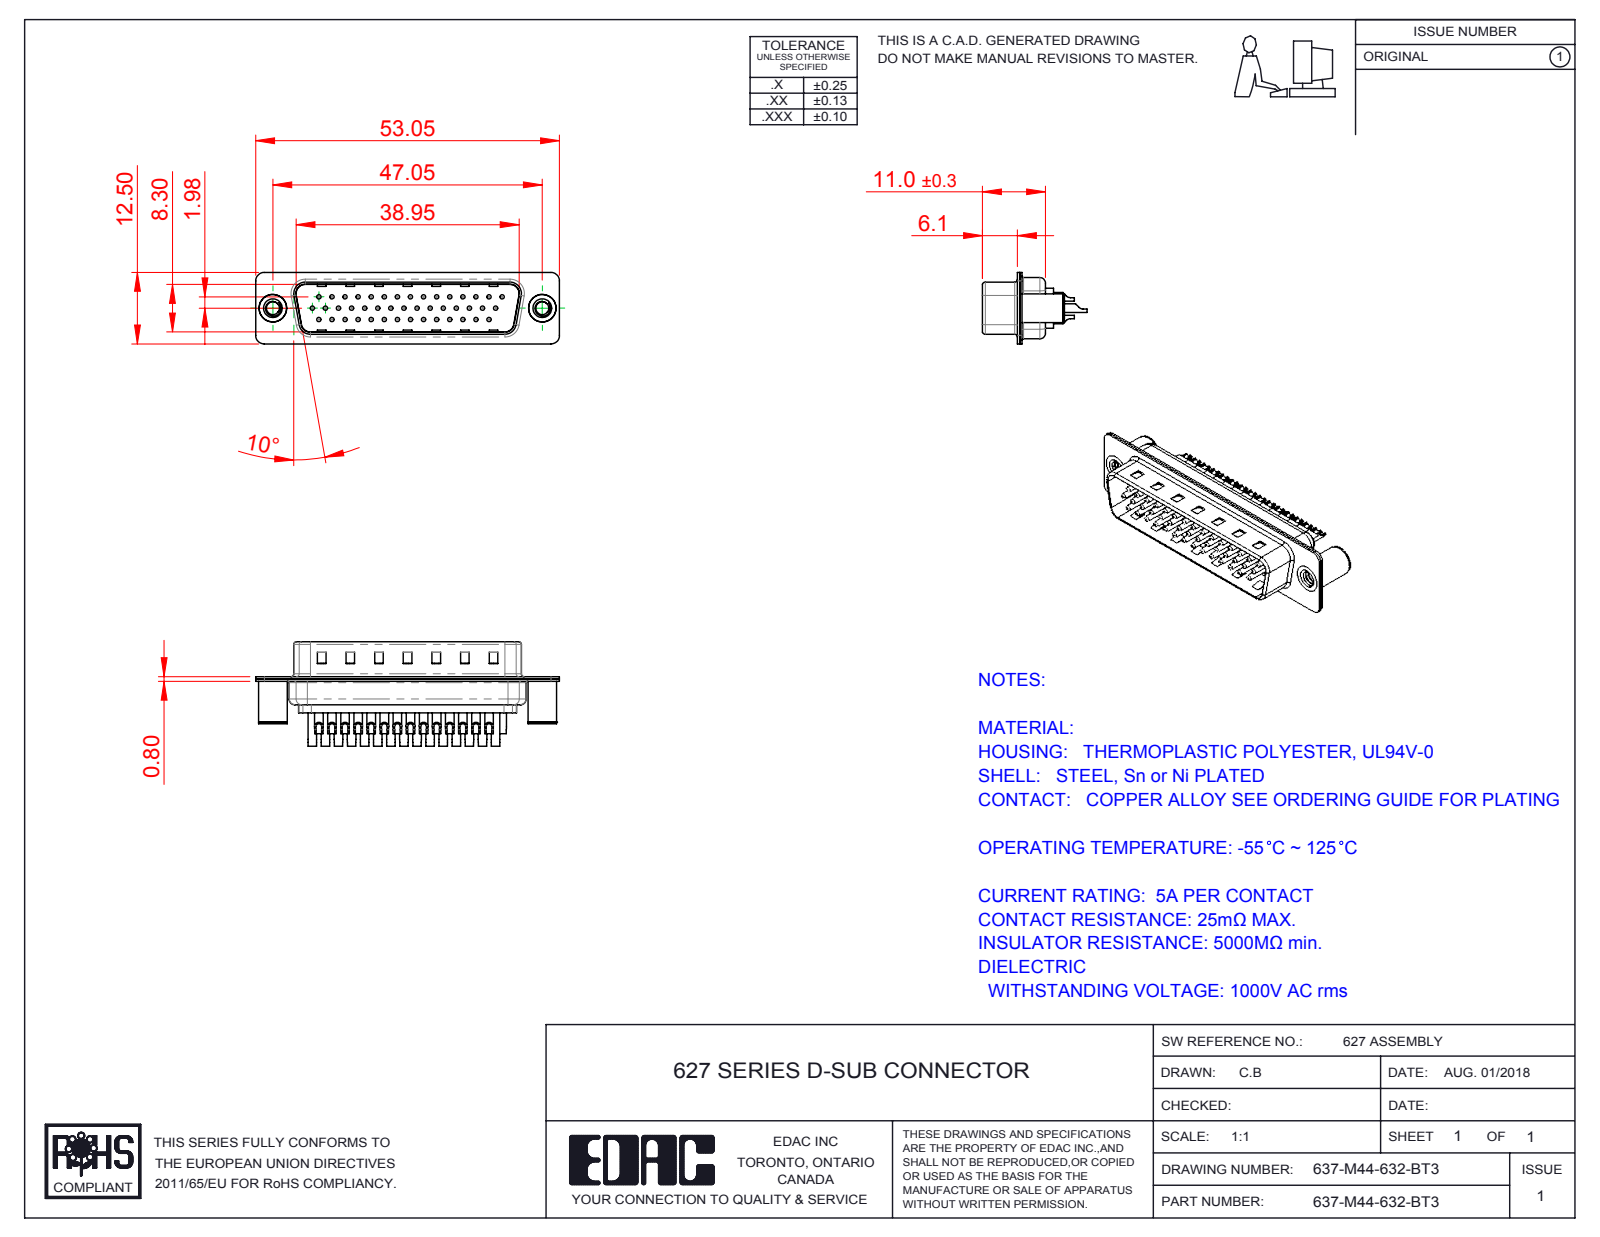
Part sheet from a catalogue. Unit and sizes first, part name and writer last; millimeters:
Units: millimetres
Overall size (bounding box): 53.05 × 18.25 × 12.5
Round holes (diameter × count): ⌀0.75 ×44, ⌀1 ×44, ⌀1.6 ×44, ⌀2 ×44, ⌀2.26 ×2, ⌀3.26 ×2, ⌀4 ×2, ⌀4.8 ×2
Round bosses / shafts (diameter × count): ⌀1.5 ×44, ⌀2 ×3, ⌀0.75 ×3, ⌀5 ×2, ⌀4.9 ×2
Partial cylindrical surfaces — rounded edges, fillets, slot ends (radius × count): R1.5 ×16, R2 ×12, R0.5 ×8, R1.6 ×8, R1 ×7, R0.25 ×4, R0.6 ×4, R0.65 ×4
Main face-to-face distances: 0.4, 0.8, 9.5, 9.1, 8.7, 9.9, 0.75, 0.35, 1.1, 1.2
Hole centre spacings: 2.28, 3.96, 2.29, 4.57, 8.24, 6.86, 11.43, 14.99
Volume: 3 097 mm³ · Surface area: 9 268 mm²
Bodies: 49 solids, 2038 faces (567 planar, 865 cylindrical, 606 other)
Part name (STEP PRODUCT): 637M 4-40 Threaded Board Spacer; 637M Contact Row 1_32; 637M Shell Rear_44 Contacts; 637-M44-632-BT3 (+4 more)
STEP written by: SolidWorks 2016 (CONFIG_CONTROL_DESIGN)
